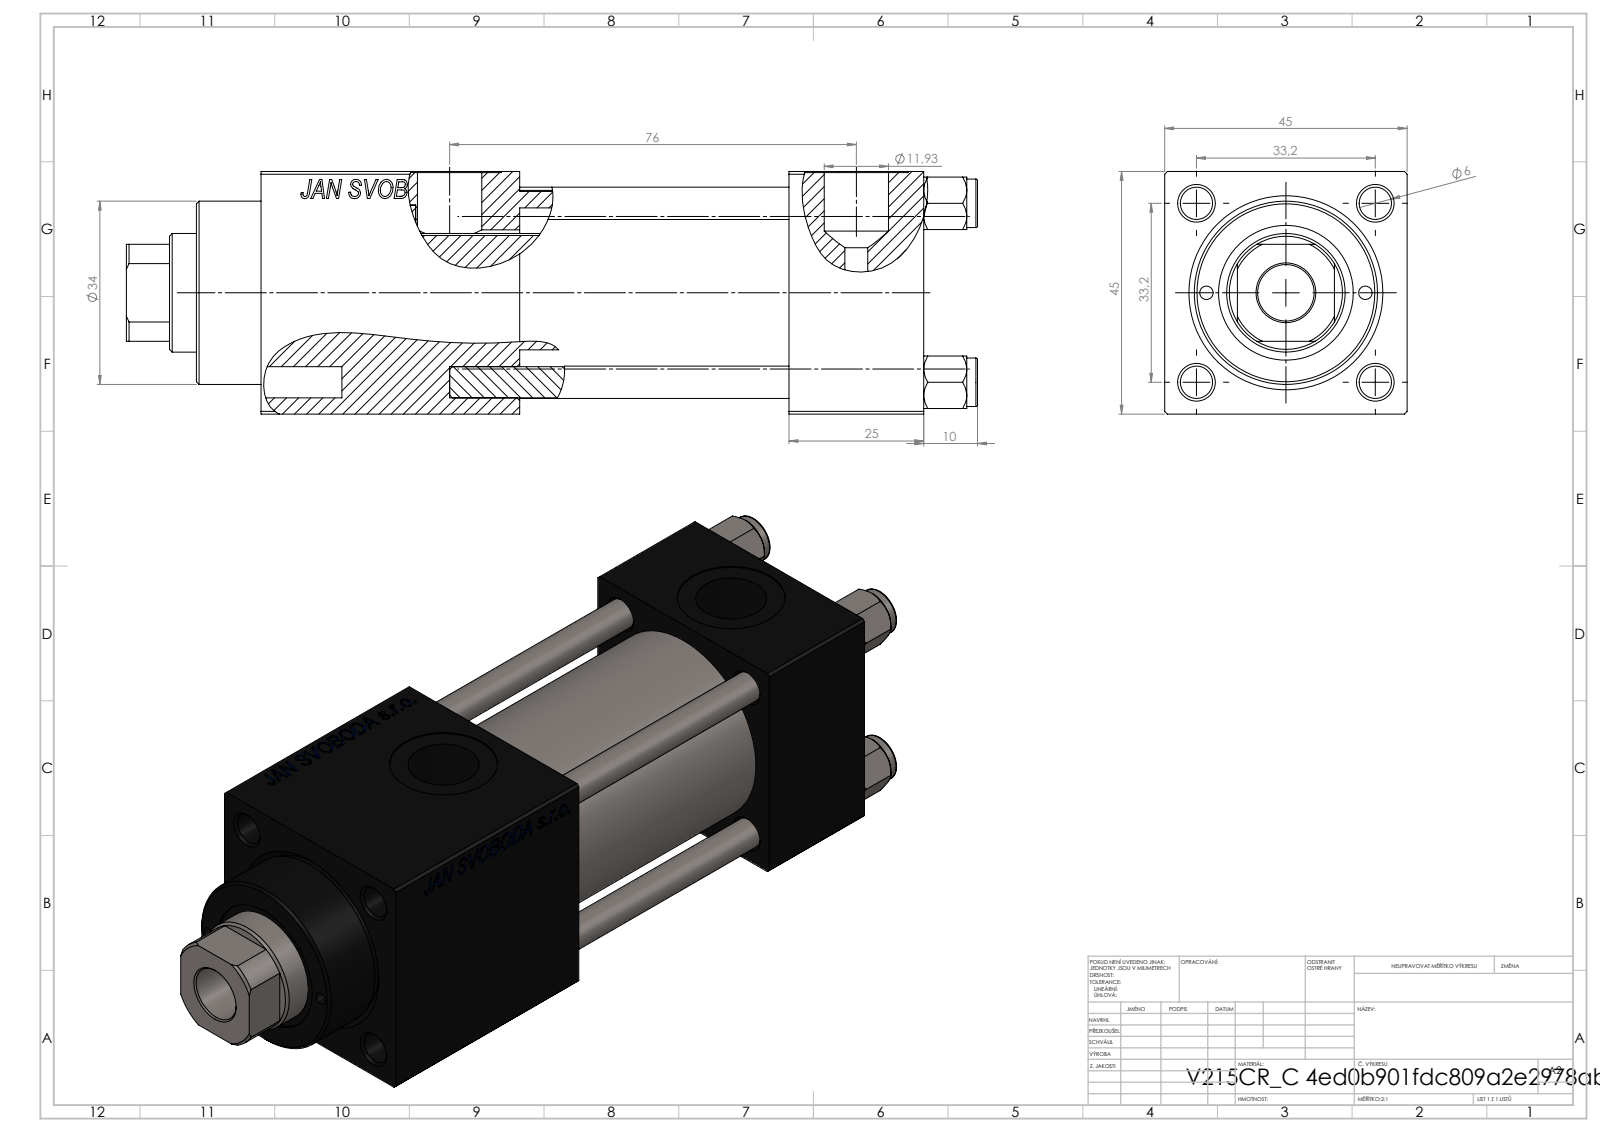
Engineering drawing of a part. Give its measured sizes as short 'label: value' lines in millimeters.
name: V215_VC_A; V215CR_C_TYCINKA; NUT_M5_C; V215CR_C_Body (+1 more)
written by: SolidWorks 2019 (CONFIG_CONTROL_DESIGN)
unit: mm
bodies: 11 solids, 1154 faces (527 planar, 91 cylindrical, 536 other)
size: 158 × 45 × 45
volume: 209 612 mm³; area: 71 570 mm²
holes: 4× ⌀6, 2× ⌀2.5, 2× ⌀7, 2× ⌀13.16, 2× ⌀20, 1× ⌀10.5, 1× ⌀22, 1× ⌀24, 1× ⌀25, 1× ⌀32, 1× ⌀33
bosses: 4× ⌀9, 1× ⌀38, 1× ⌀34
rounds: 1× R10.5
face distances: 45, 25, 50, 123, 75, 98, 48, 94.3, 69.3, 19.3
hole spacings: 16.7, 23.48, 33.2, 35.47, 14.75, 46.95, 29.5, 75.5
